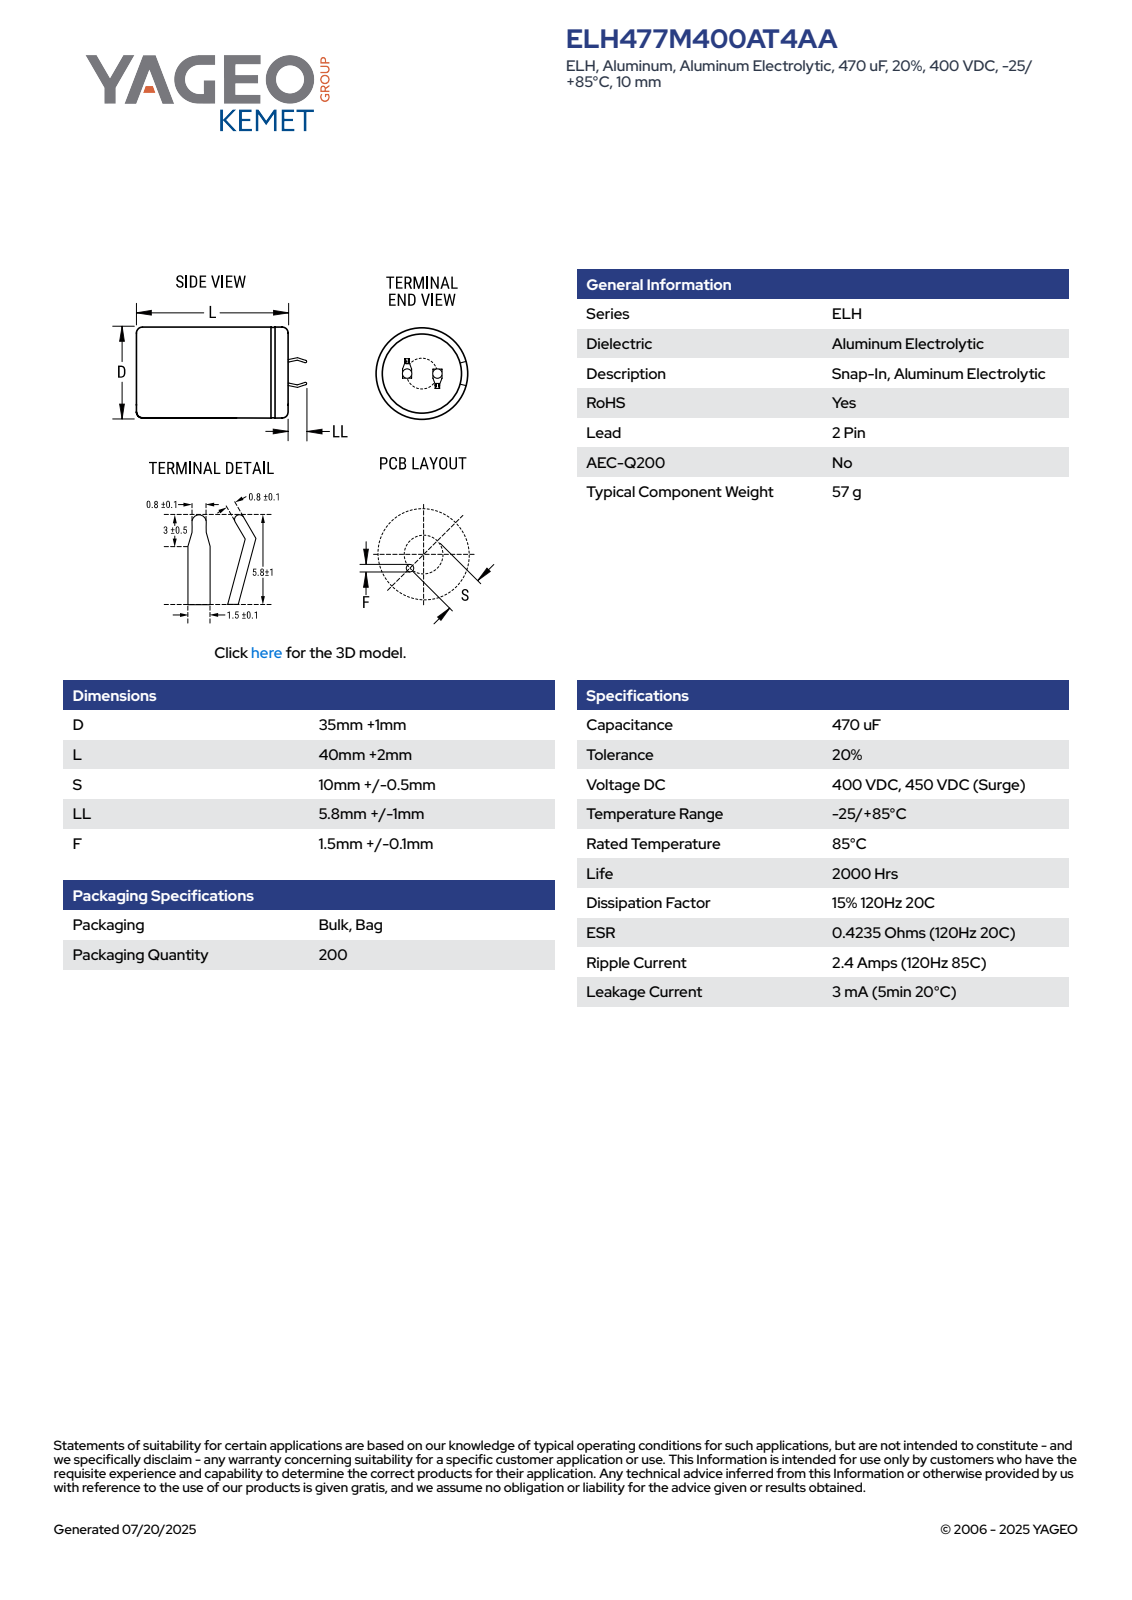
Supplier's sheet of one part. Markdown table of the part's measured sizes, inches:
| quantity | value |
| --- | --- |
| part name | CARS_K2P_35X40_D36L42S10LL6.8F1.6 |
| STEP written by | SolidWorks 2014 (AUTOMOTIVE_DESIGN) |
| units | inches |
| bodies | 1 solid, 100 faces (52 planar, 9 cylindrical, 39 other) |
| overall size | 1.921 × 1.417 × 1.417 |
| volume | 2.577 in³ |
| surface area | 10.51 in² |
| round holes (diameter × count) | 1.254 × 1 |
| round bosses / shafts (diameter × count) | 1.417 × 1 |
| partial cylindrical surfaces (radius × count) | 0.708 × 1 |
| main face-to-face distances | 1.653, 0.024, 1.673, 0.02, 0.279, 0.3, 0.03, 0.053, 0.302, 0.255 |
